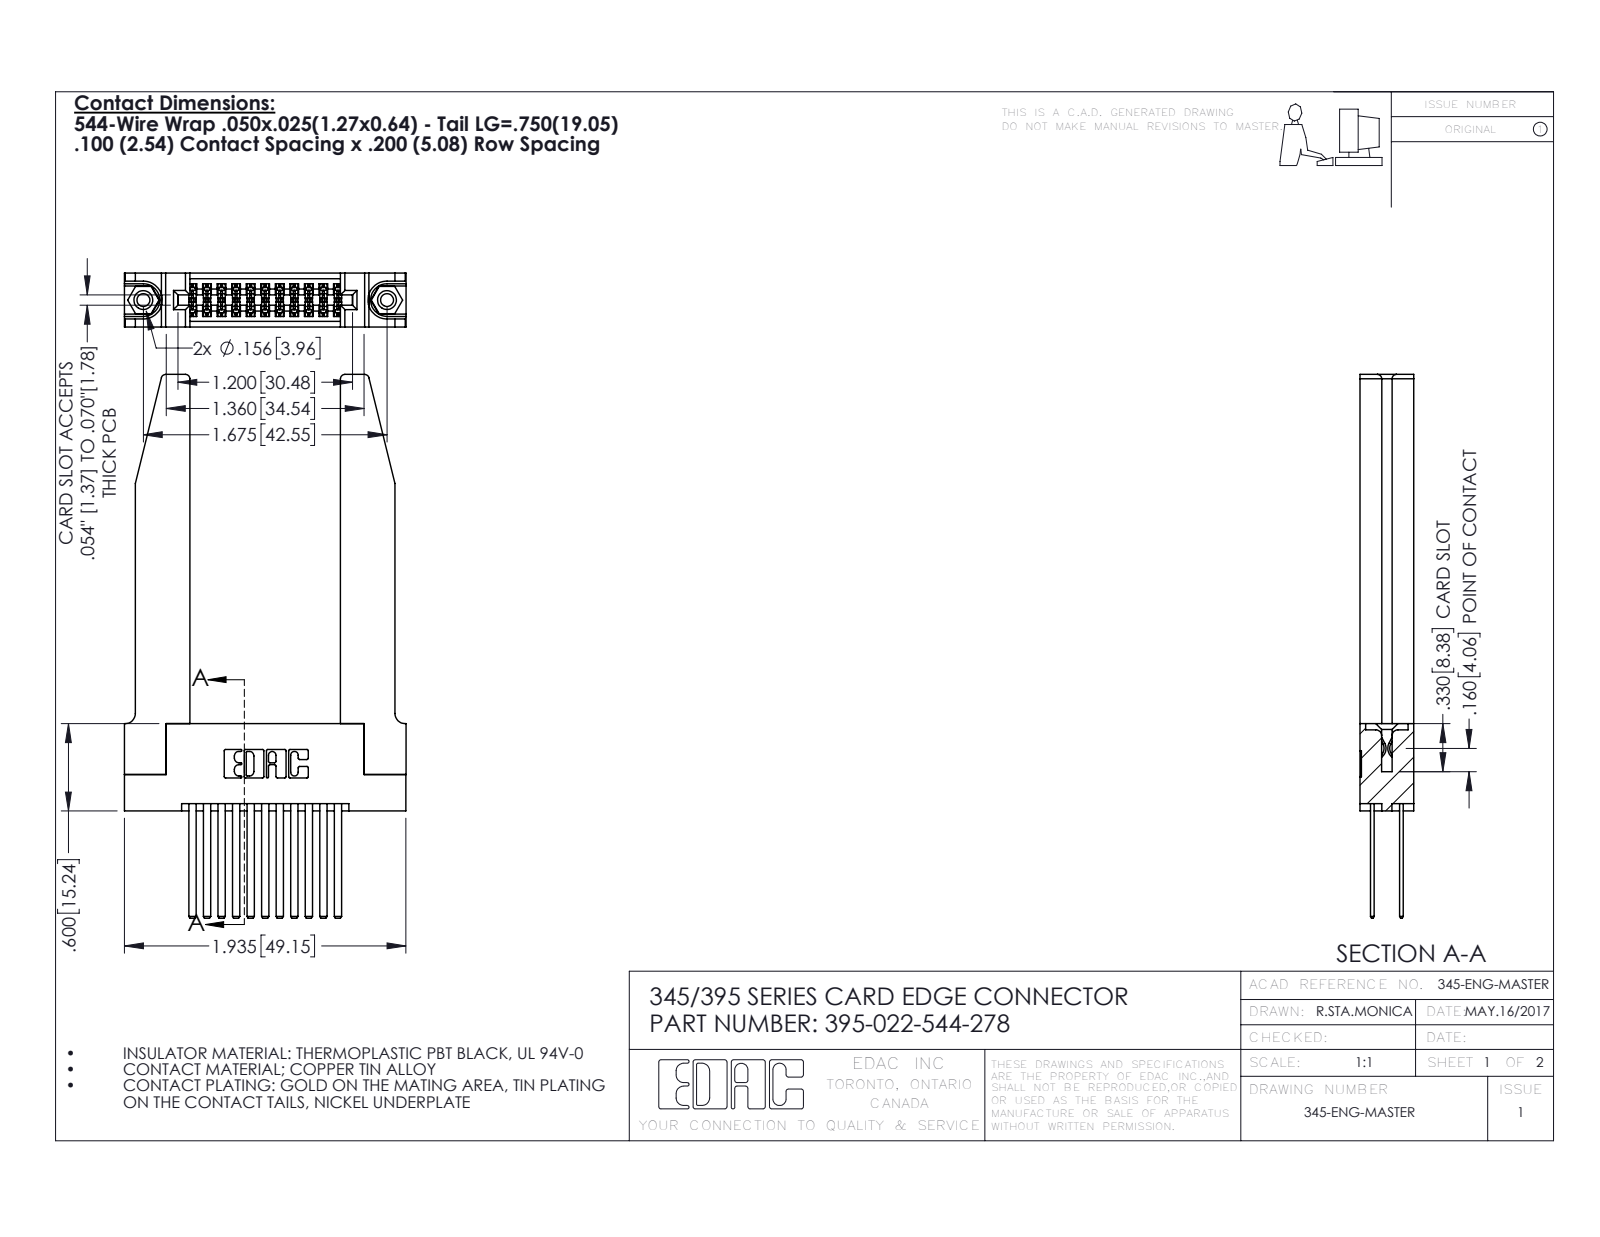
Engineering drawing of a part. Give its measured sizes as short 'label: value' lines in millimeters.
name: 395-022-544-278; 345-220-078_345-220-078; 345-250-001_345-250-001-102; 345 Part_Flush Mounting Lugs - 0.156 Dia-TH (+1 more)
written by: SolidWorks 2016 (CONFIG_CONTROL_DESIGN)
unit: mm
bodies: 27 solids, 1328 faces (860 planar, 416 cylindrical, 52 other)
size: 94.9 × 49.2 × 9.4
volume: 12 600 mm³; area: 14 230 mm²
holes: 2× ⌀2.3, 2× ⌀3.2, 2× ⌀4, 1× ⌀1.6
bosses: 2× ⌀3.9
rounds: 33× R0.2, 22× R0.3, 8× R0.8, 6× R0.2, 6× R0.8, 3× R0.7, 2× R0.4, 2× R0.5
face distances: 9.4, 1.8, 7.6, 5.1, 2.5, 6.9, 0.6, 5.7, 3.8, 3.8
hole spacings: 6.9, 36.7, 42.5
